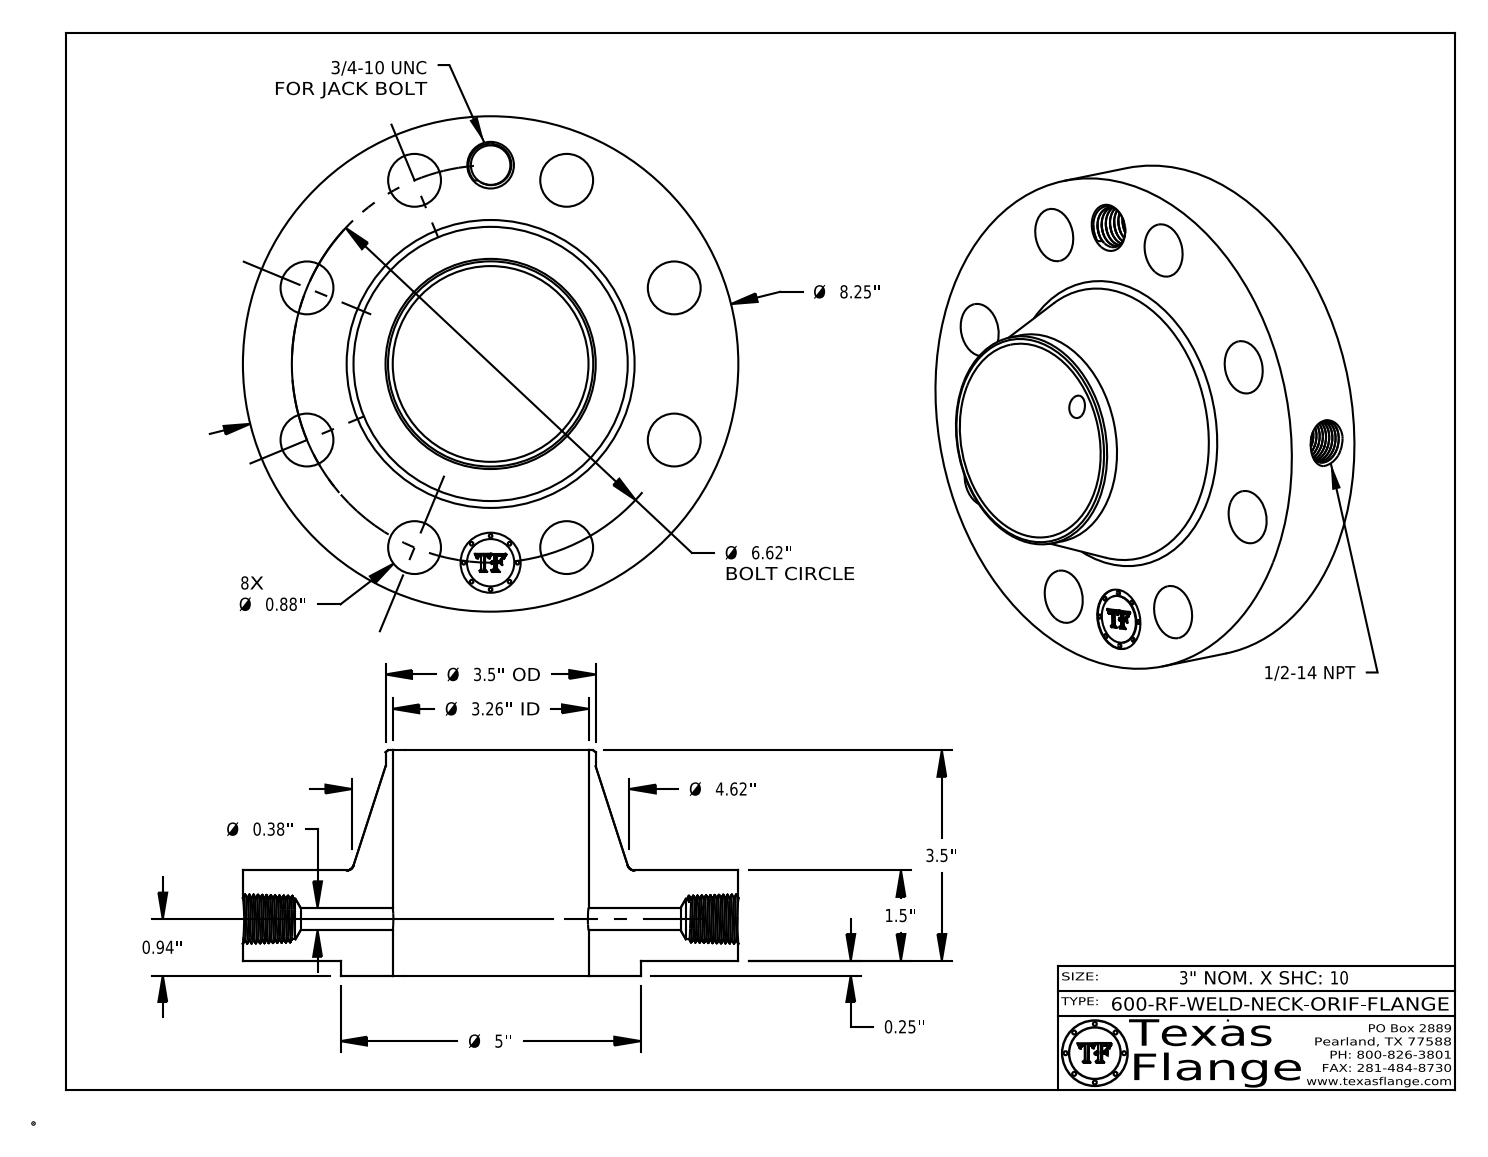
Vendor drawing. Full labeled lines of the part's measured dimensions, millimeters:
Part name (STEP PRODUCT): 600-RF-WELD-NECK
STEP written by: CATIA V5 STEP AP214 (AUTOMOTIVE_DESIGN)
Units: millimetres
Bodies: 1 solid, 769 faces (369 planar, 92 cylindrical, 308 other)
Overall size (bounding box): 209.6 × 209.6 × 95.3
Volume: 1 146 000 mm³ · Surface area: 146 700 mm²
Round holes (diameter × count): ⌀22.4 ×8, ⌀9.5 ×1, ⌀16.7 ×1, ⌀17.1 ×1, ⌀25.4 ×1, ⌀82.8 ×1
Round bosses / shafts (diameter × count): ⌀1.5 ×8, ⌀209.6 ×1, ⌀127 ×1, ⌀88.9 ×1, ⌀20 ×1
Main face-to-face distances: 38.1, 6.4, 44.5, 95.3, 88.9, 50.8, 0.4, 44.1, 37.7, 51.2
Hole centre spacings: 84.1, 118.9, 155.3, 168.1, 32.8, 64.3, 64.3, 93.4
